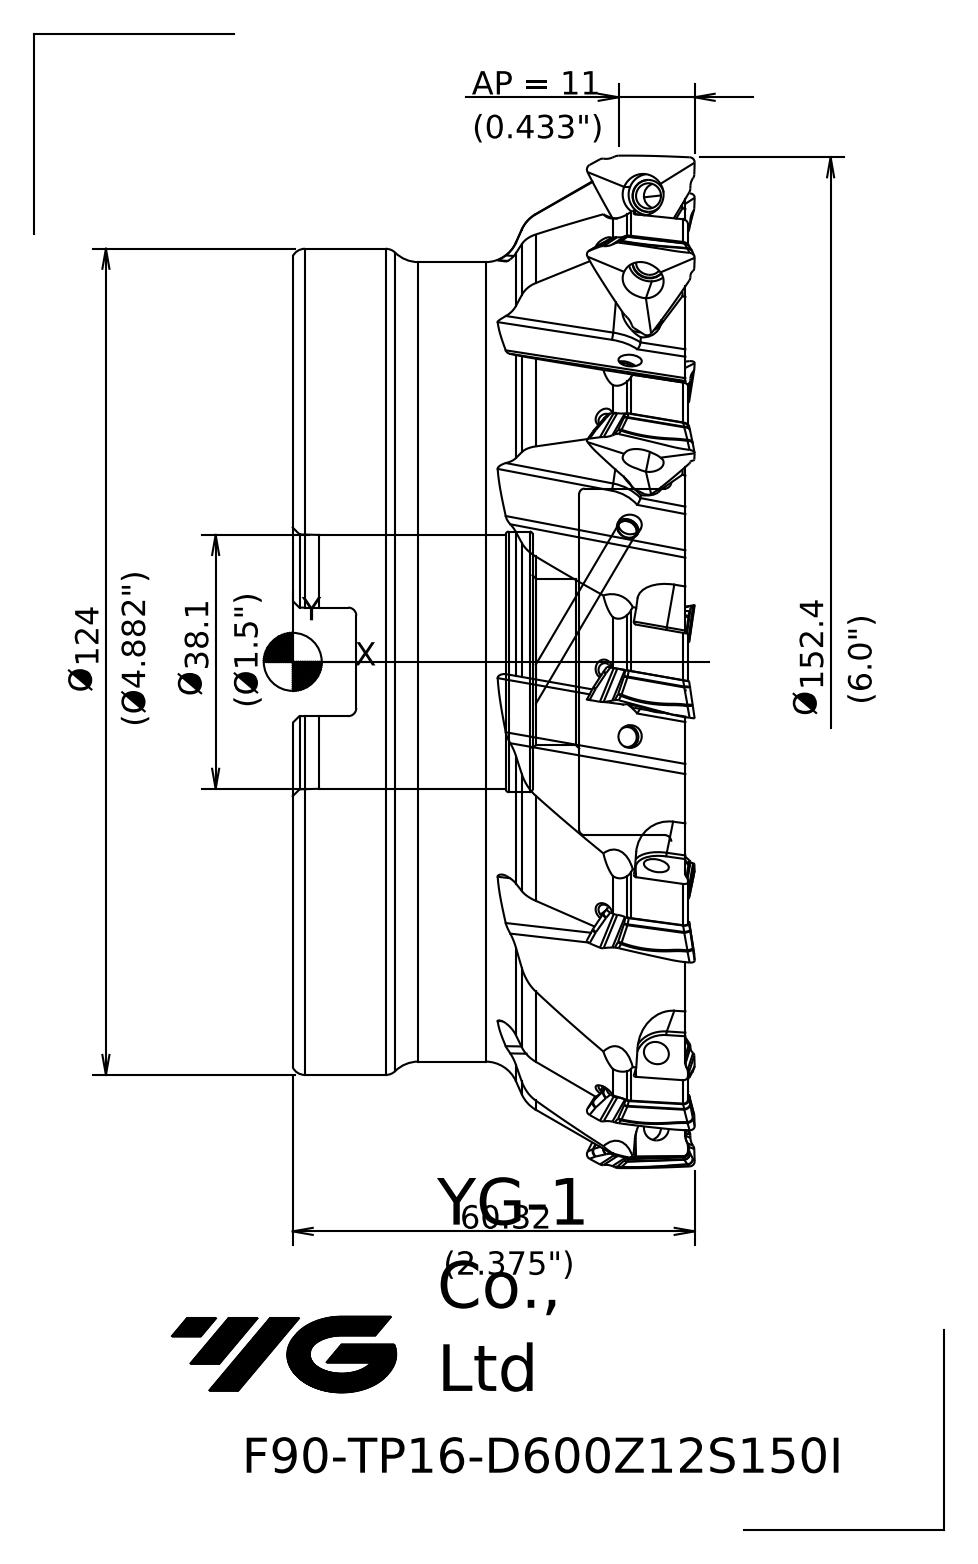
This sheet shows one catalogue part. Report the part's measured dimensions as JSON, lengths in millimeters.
{"part_name": "10224CC45D94rgeh", "step_written_by": "SIEMENS PLM Software NX 10.0 (AP203_CONFIGURATION_CONTROLLED_3D_DESIGN_OF_MECHANICAL_PARTS_AND_ASSEMBLIES_MIM_LF)", "units": "millimeters", "bodies": {"solids": 1, "faces": 76, "planar": 18, "cylindrical": 10, "other": 48}, "overall_size": [152.54, 152.54, 60.33], "volume_mm3": 697227, "surface_area_mm2": 85175, "round_holes": [[25, 1], [38.1, 1], [39.1, 1], [52, 1]], "round_bosses_or_shafts": [[124, 1], [120, 1]], "partial_cylinders_radius": [[1.2, 2]], "face_to_face_distances": [58.93, 2.1, 56.83, 15.93, 13.83, 43, 49.39, 47.29, 33.46, 9.54]}
